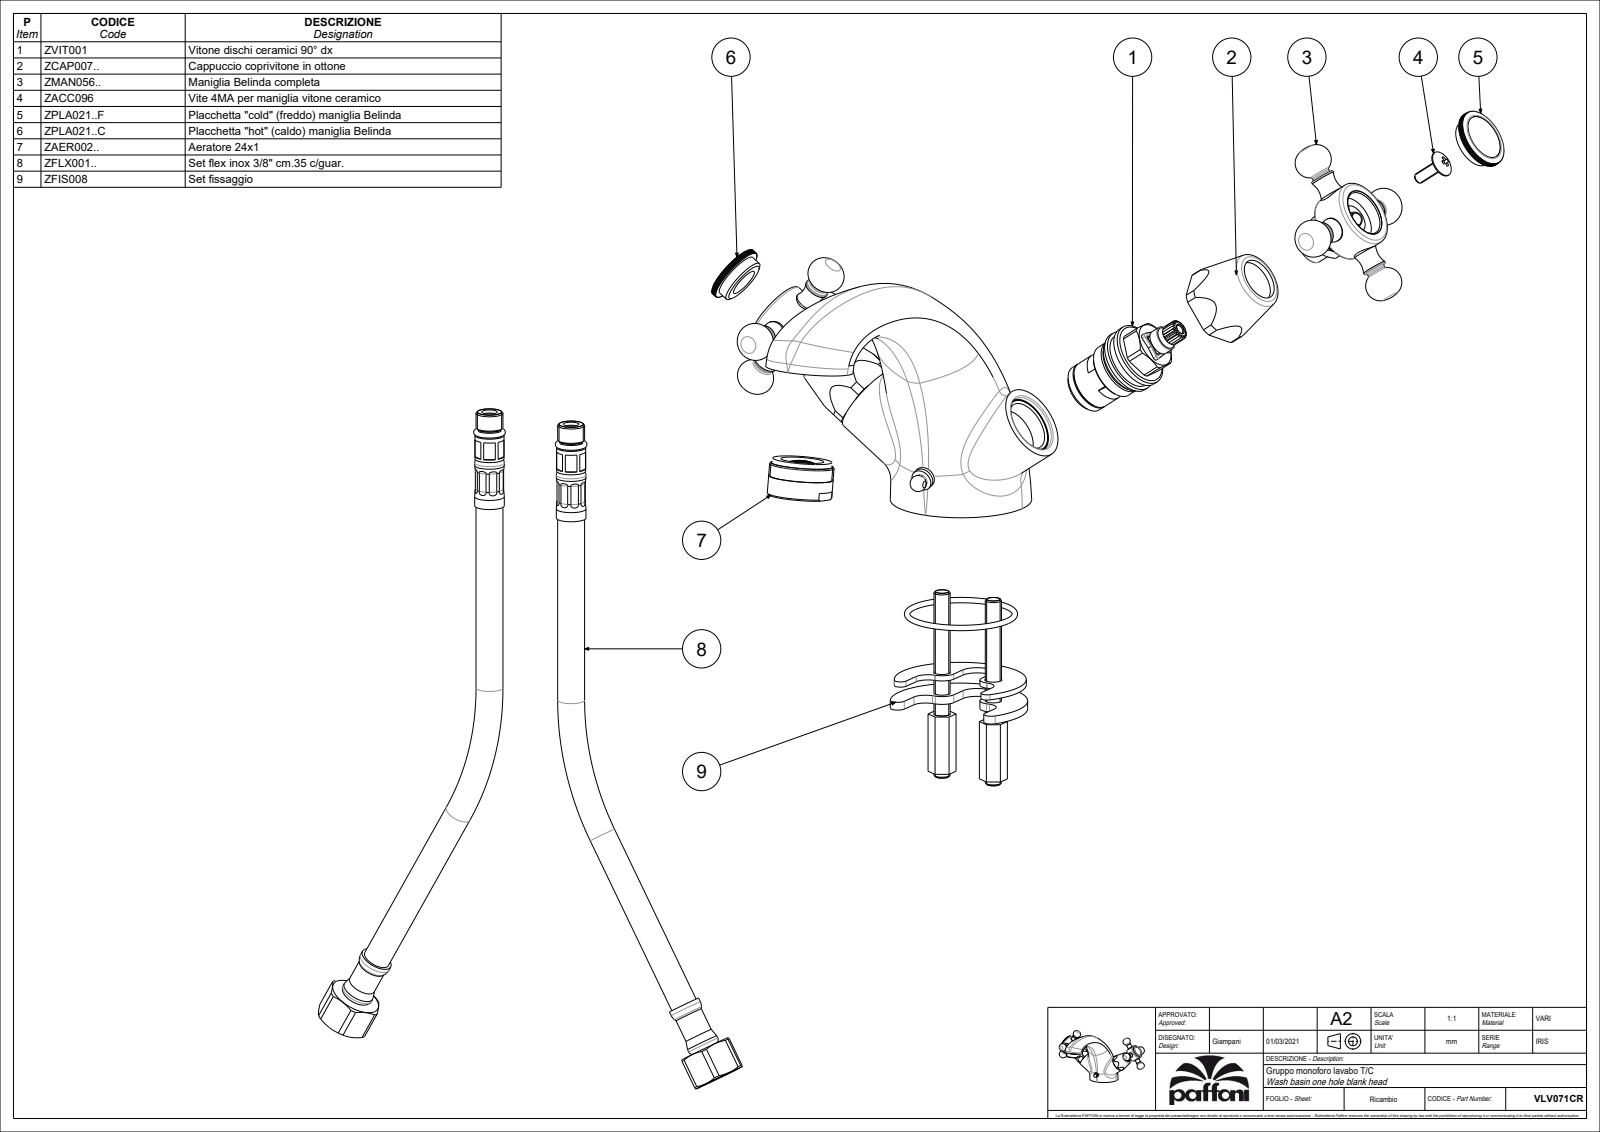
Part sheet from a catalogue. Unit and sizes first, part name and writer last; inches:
Units: inches
Overall size (bounding box): 7.094 × 6.094 × 3.88
Round holes (diameter × count): ⌀0.098 ×1
Round bosses / shafts (diameter × count): ⌀0.354 ×6, ⌀0.276 ×6, ⌀1.083 ×2, ⌀0.984 ×2, ⌀0.551 ×2, ⌀0.512 ×2, ⌀0.945 ×1, ⌀0.315 ×1
Partial cylindrical surfaces — rounded edges, fillets, slot ends (radius × count): R0.433 ×2, R0.571 ×2
Main face-to-face distances: 1.386, 1.937, 0.551, 0.157, 1.043, 0.945, 0.441, 0.992, 2.036, 1.091
Bodies: 0 solids, 913 faces (445 planar, 284 cylindrical, 184 other)
Part name (STEP PRODUCT): VLV071CR
STEP written by: CREO PARAMETRIC BY PTC INC, 2020044 (CONFIG_CONTROL_DESIGN)
